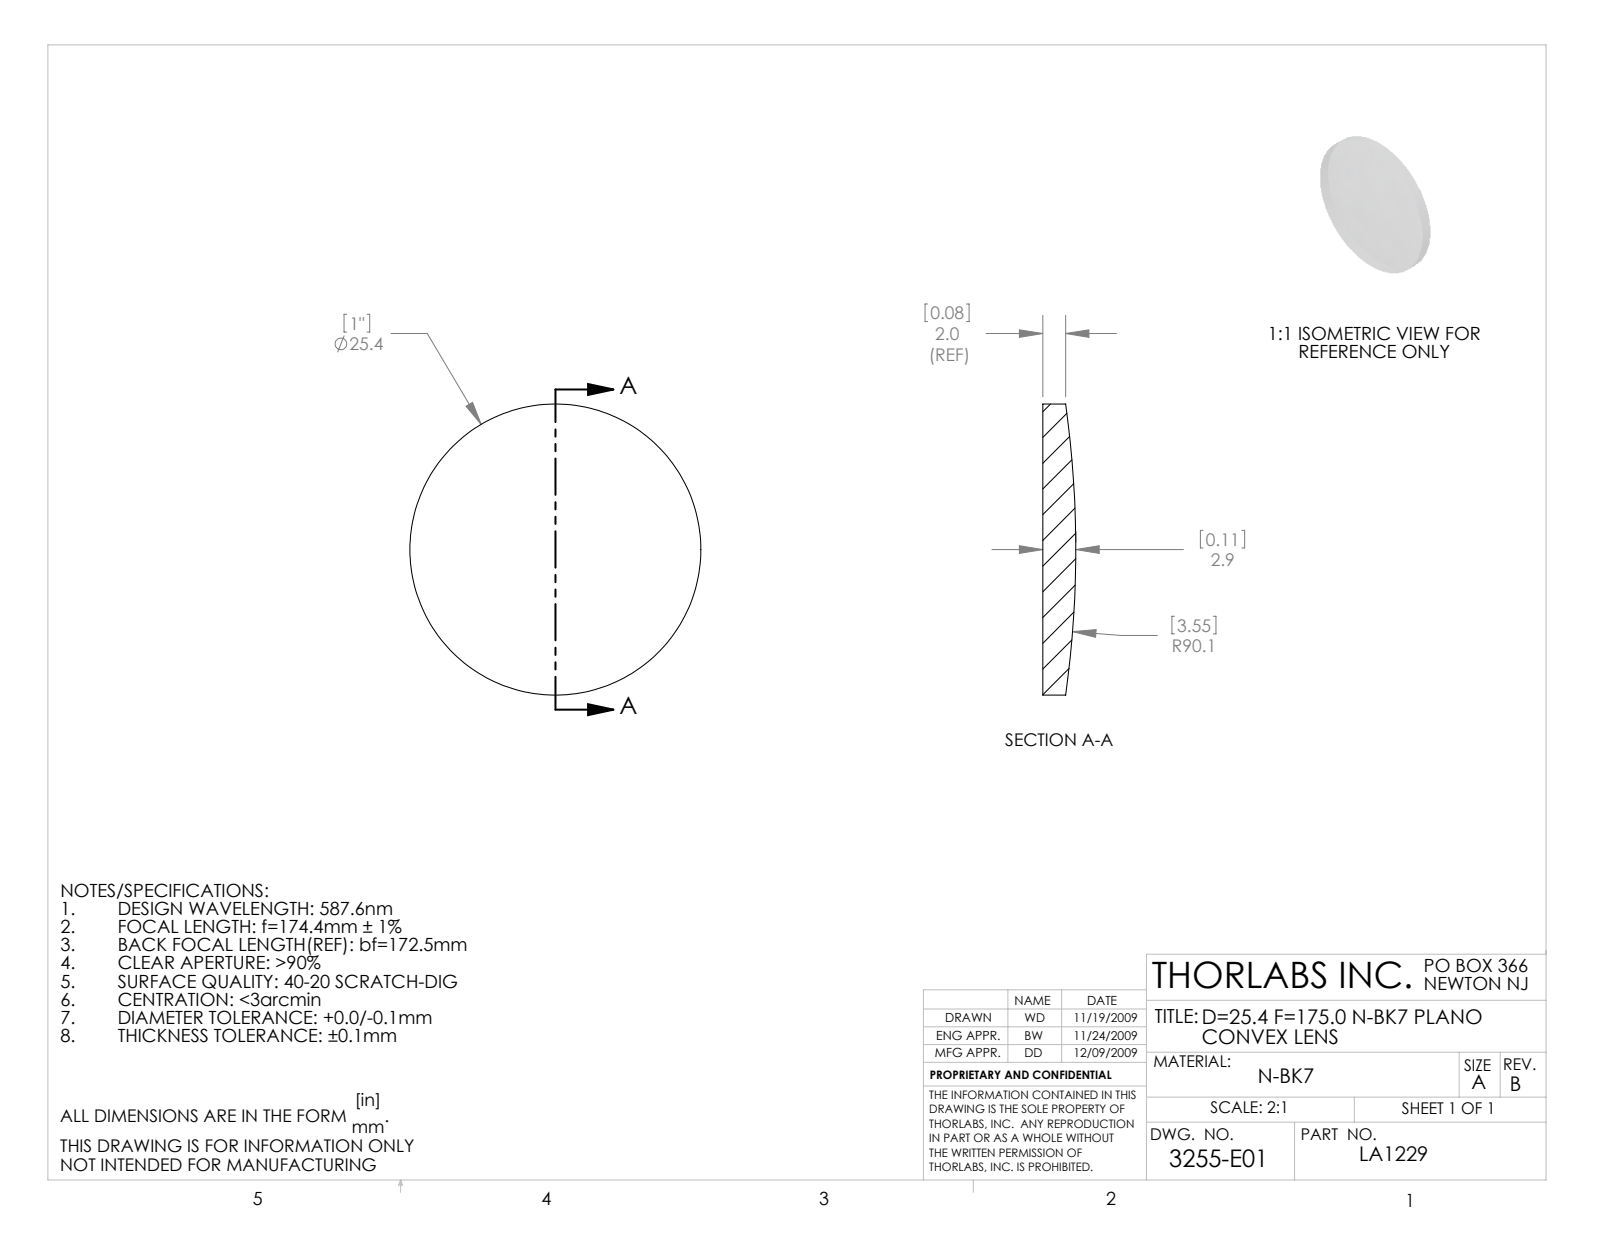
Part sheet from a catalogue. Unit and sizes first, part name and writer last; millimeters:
Units: millimetres
Overall size (bounding box): 25.4 × 25.4 × 2.89
Round bosses / shafts (diameter × count): ⌀25.4 ×1
Volume: 1 237 mm³ · Surface area: 1 175 mm²
Bodies: 1 solid, 5 faces (1 planar, 2 cylindrical, 2 other)
Part name (STEP PRODUCT): 3255-E0W
STEP written by: SolidWorks 2009 (AUTOMOTIVE_DESIGN)
